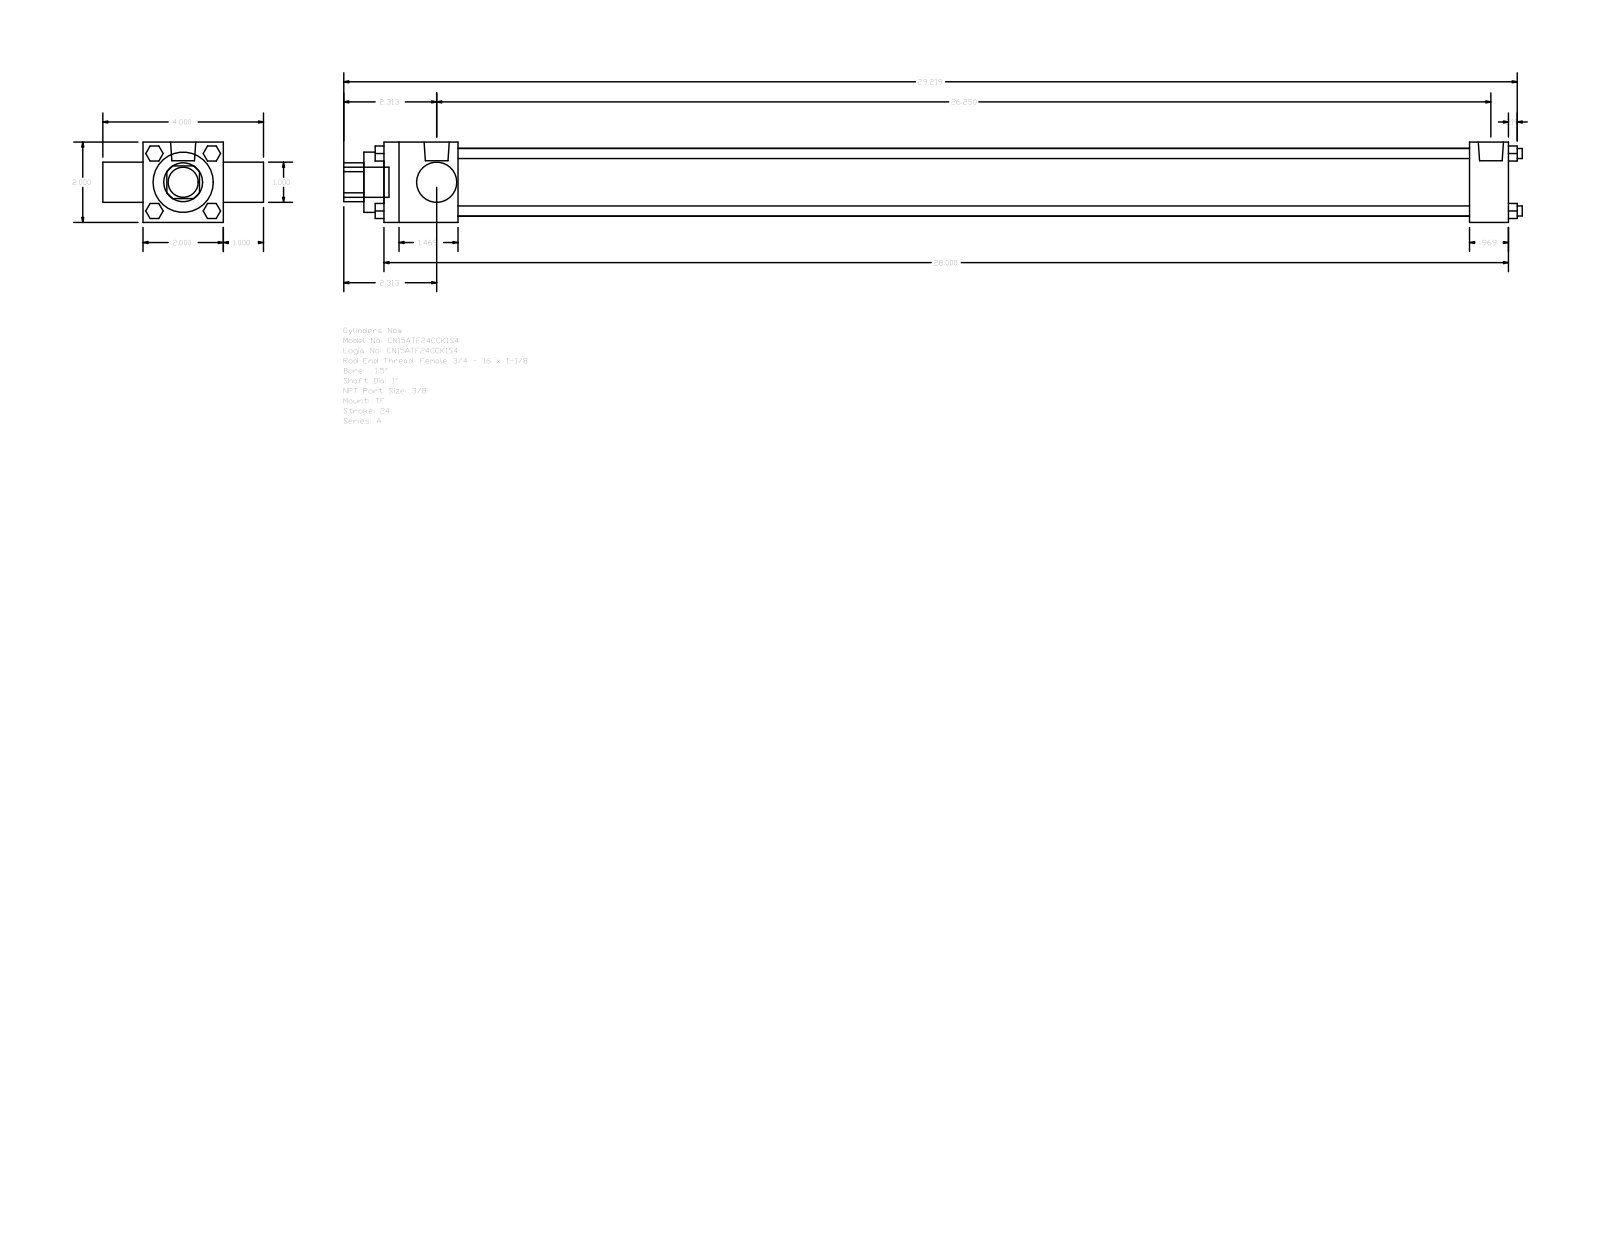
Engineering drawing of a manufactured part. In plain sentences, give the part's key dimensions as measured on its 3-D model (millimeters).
The part is named "A_TF__0150_1". Its 3-D file was written by "GSSL Pune (CONFIG_CONTROL_DESIGN)". It is 0 solids with 120 faces: 92 planar, 28 cylindrical and 0 other. Overall it measures 745.33 by 101.6 by 50.8 millimeters. Round holes: 2 of diameter 25.4, 1 of diameter 38.1, 1 of diameter 42.93. Round bosses or shafts: 4 of diameter 6.35, 3 of diameter 5.56, 2 of diameter 15.93, 1 of diameter 19.05. Partial cylindrical surfaces (rounded edges, fillets, slot ends): 1 of radius 12.29. The main face-to-face distances are 50.8, 25.4, 711.2, 76.2, 46.83, 686.59, 639.76, 664.37, 24.61, 12.7.
